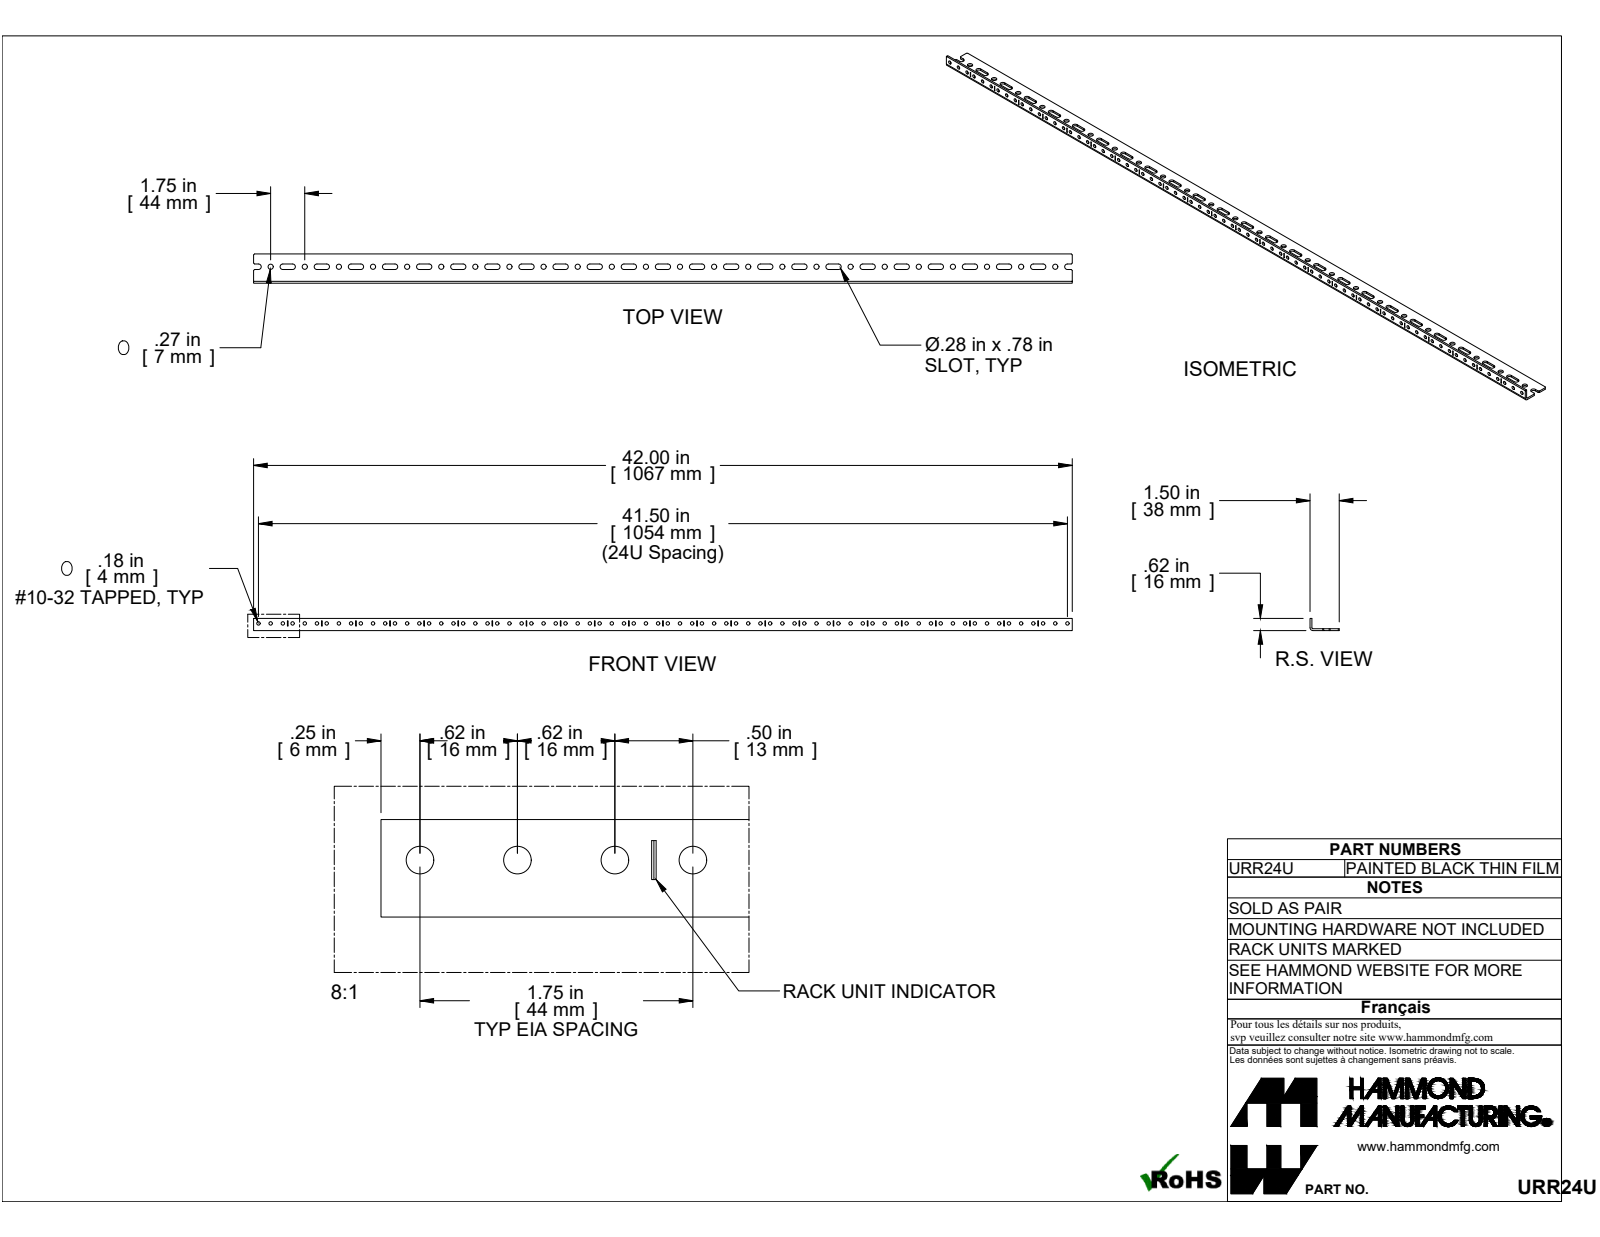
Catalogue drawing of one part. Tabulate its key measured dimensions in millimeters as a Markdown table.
| quantity | value |
| --- | --- |
| part name | COM57213-24 |
| STEP written by | ST-DEVELOPER v16.7 (AUTOMOTIVE_DESIGN) |
| units | millimeters |
| bodies | 1 solid, 304 faces (158 planar, 146 cylindrical, 0 other) |
| overall size | 1066.8 × 38.1 × 15.88 |
| volume | 117 604 mm³ |
| surface area | 109 421 mm² |
| round holes (diameter × count) | 4.5 × 72, 6.76 × 24 |
| partial cylindrical surfaces (radius × count) | 3.57 × 48, 1.22 × 1, 3.63 × 1 |
| main face-to-face distances | 2.41, 15.88, 13.47, 38.1, 35.69, 17.84, 24.98, 15.43, 22.57, 7.14 |
| hole center spacings | 44.45, 133.35, 88.9, 177.8, 266.7, 222.25, 311.15, 88.91 |
